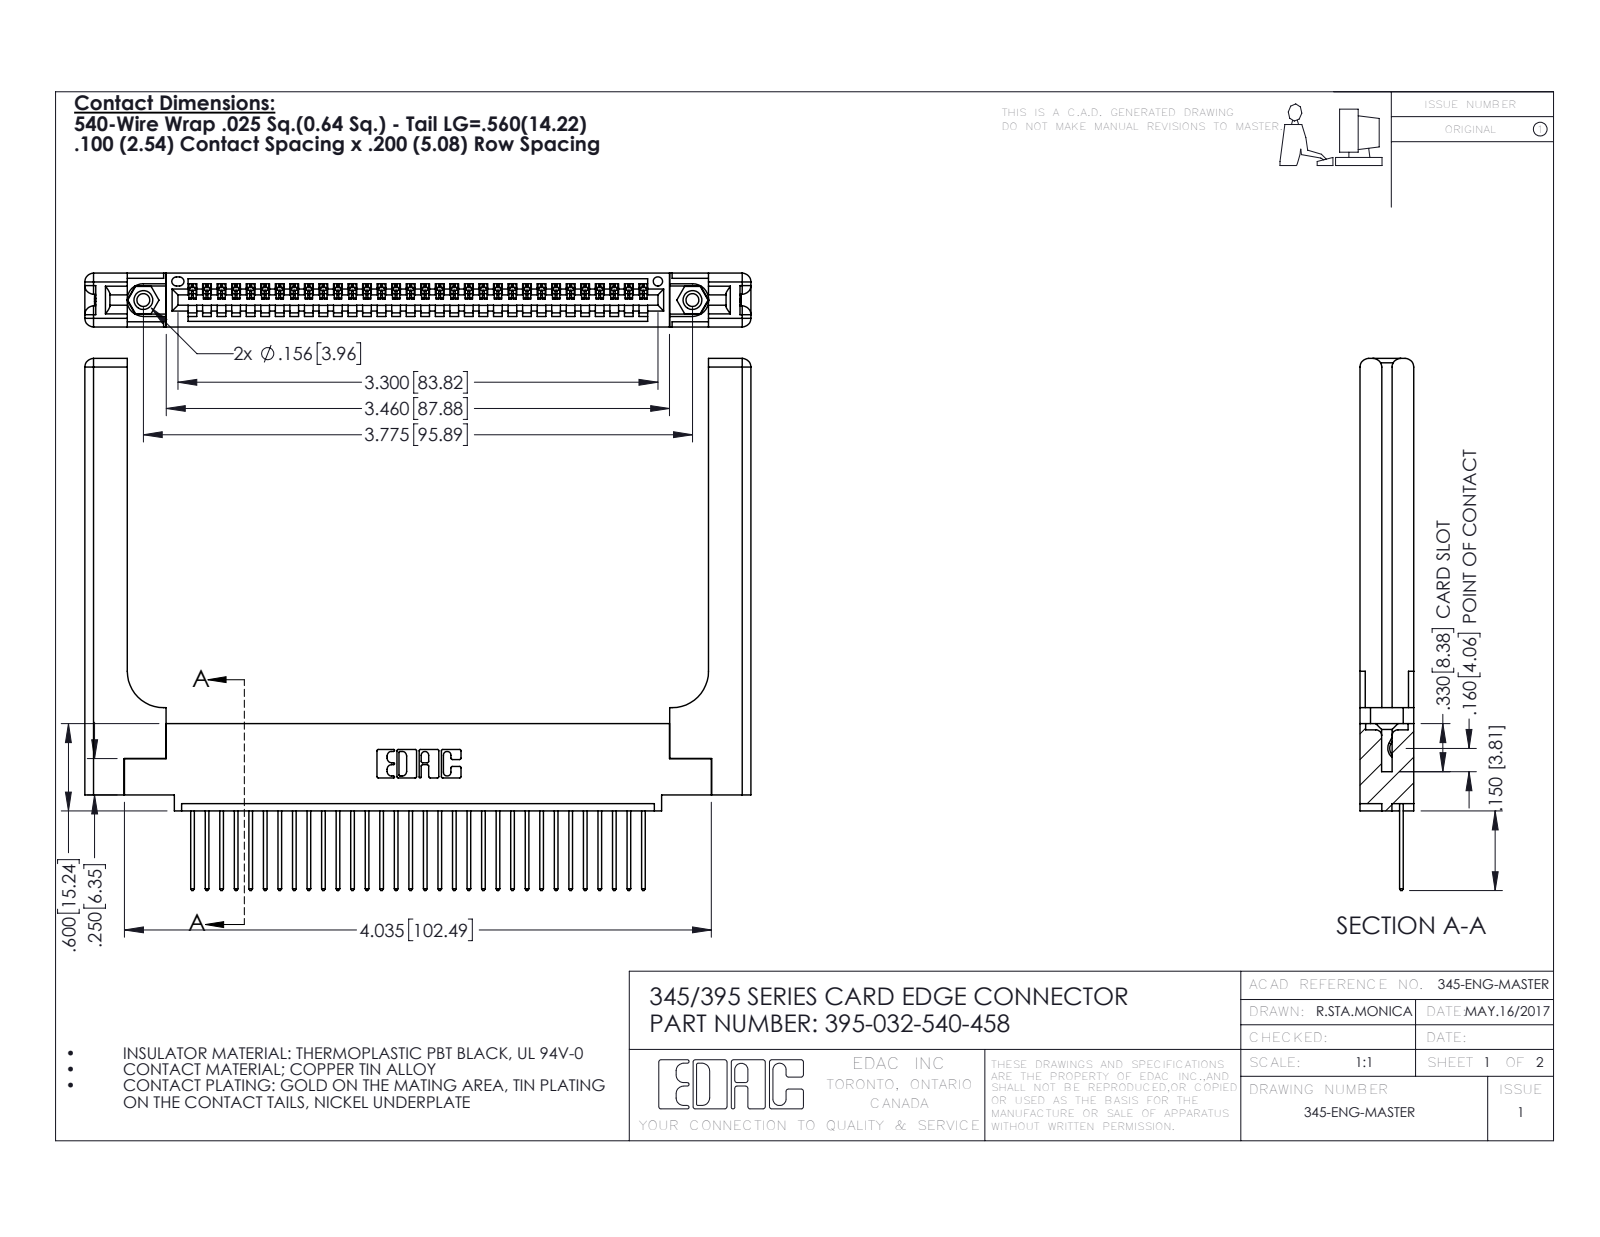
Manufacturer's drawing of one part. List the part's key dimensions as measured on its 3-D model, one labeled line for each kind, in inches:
Part name (STEP PRODUCT): 395-032-540-458; 345 Part_0.110 Offset - 0.156 Dia-TH; 345-250-001_345-250-001-102; 345-220-058_345-220-058 (+1 more)
STEP written by: SolidWorks 2016 (CONFIG_CONTROL_DESIGN)
Units: inches
Bodies: 37 solids, 2242 faces (1512 planar, 670 cylindrical, 60 other)
Overall size (bounding box): 4.579 × 3.657 × 0.37
Volume: 1.186 in³ · Surface area: 31.15 in²
Round holes (diameter × count): ⌀0.089 ×2, ⌀0.125 ×2, ⌀0.156 ×2, ⌀0.064 ×1
Round bosses / shafts (diameter × count): ⌀0.155 ×2
Partial cylindrical surfaces — rounded edges, fillets, slot ends (radius × count): R0.006 ×64, R0.01 ×64, R0.01 ×22, R0.06 ×16, R0.007 ×6, R0.031 ×6, R0.026 ×3, R0.03 ×2
Main face-to-face distances: 0.37, 0.072, 0.298, 0.098, 0.272, 0.025, 0.2, 0.148, 0.15, 0.077
Hole centre spacings: 0.27, 3.54, 3.775
